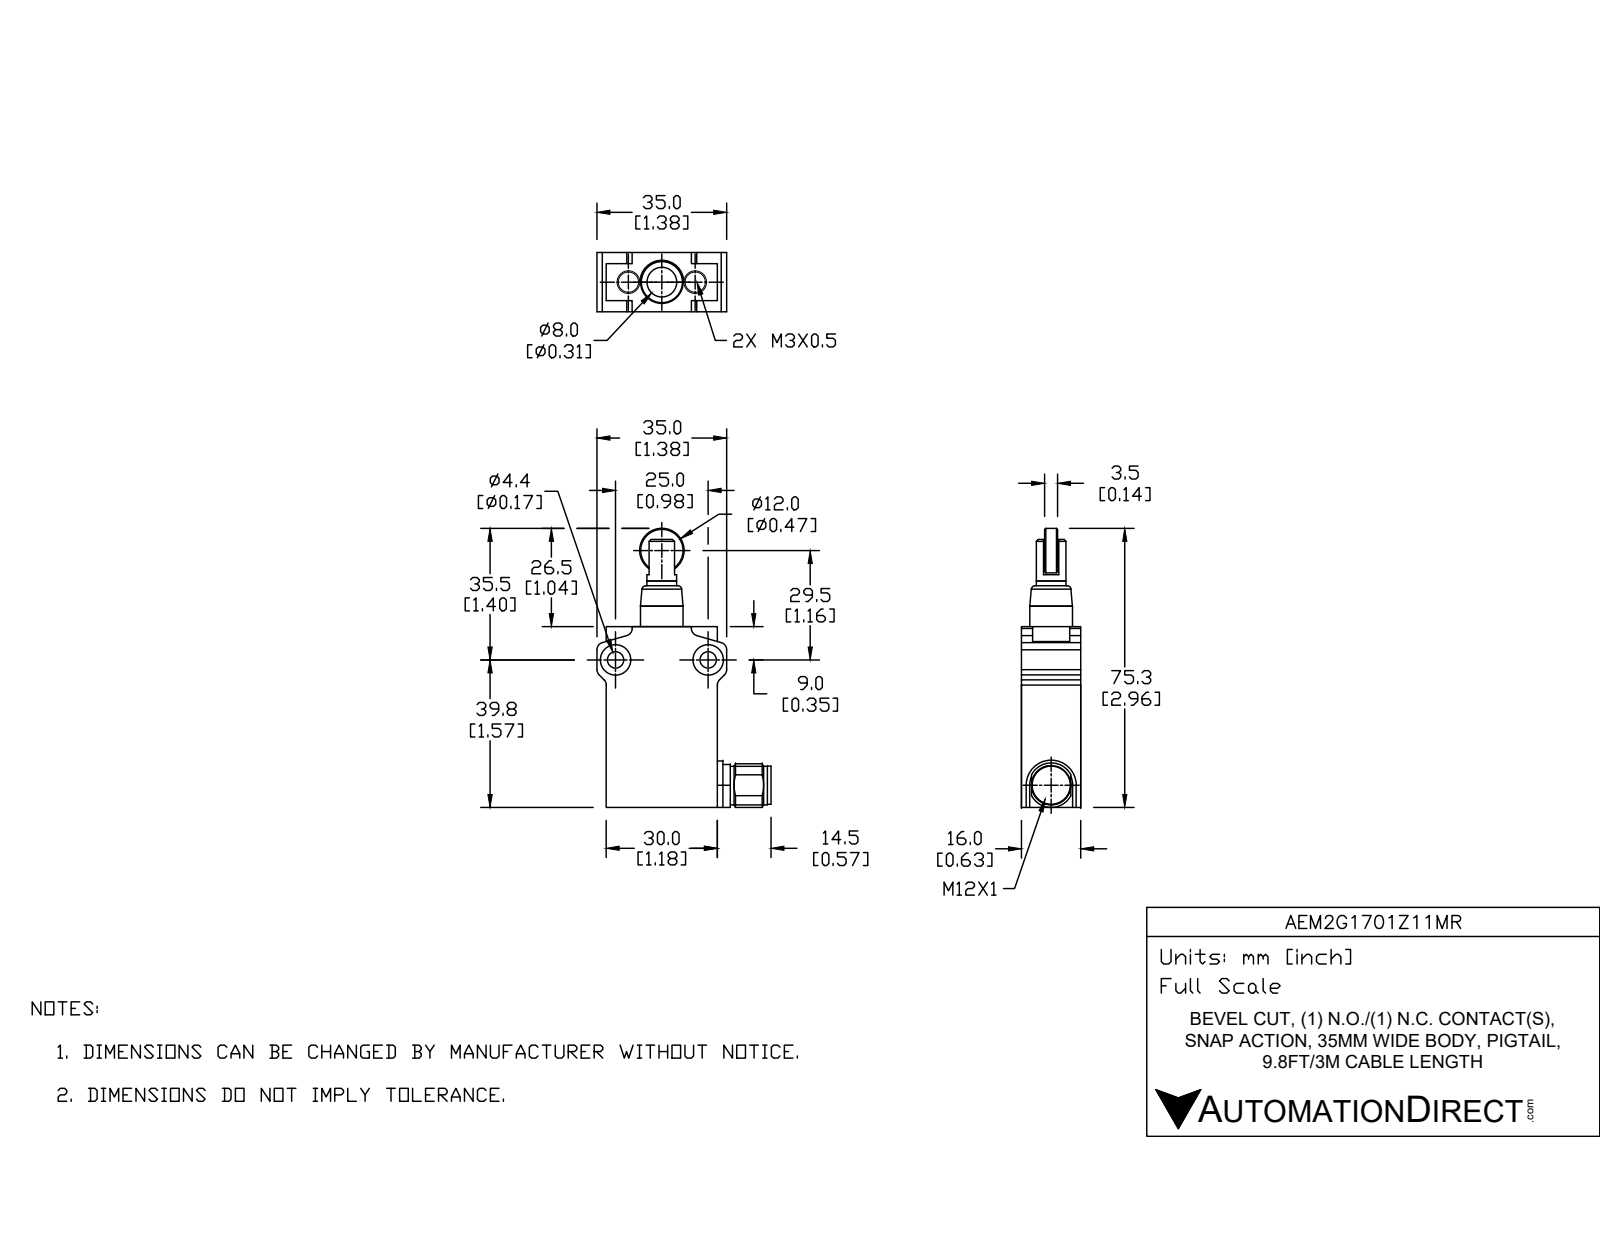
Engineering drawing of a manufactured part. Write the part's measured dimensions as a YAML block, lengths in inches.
part_name: "AEM2G1701Z11MR"
step_written_by: "SolidWorks 2019 (AUTOMOTIVE_DESIGN)"
units: inches
bodies: {solids: 6, faces: 152, planar: 60, cylindrical: 52, other: 40}
overall_size: [3.091, 1.831, 0.63]
volume: 1.716
surface_area: 14.78
round_holes:
  - {diameter: 0.118, count: 2}
  - {diameter: 0.173, count: 2}
  - {diameter: 0.323, count: 2}
round_bosses_or_shafts:
  - {diameter: 0.472, count: 2}
  - {diameter: 0.453, count: 1}
  - {diameter: 0.417, count: 1}
  - {diameter: 0.406, count: 1}
  - {diameter: 0.315, count: 1}
  - {diameter: 0.236, count: 1}
  - {diameter: 0.22, count: 1}
partial_cylinders:
  - {radius: 0.079, count: 8}
  - {radius: 0.256, count: 1}
face_to_face_distances: [0.63, 1.181, 2.047, 0.472, 1.858, 0.189, 0.157, 0.234, 0.238, 0.098]
hole_center_spacings: [0.748, 0.984]
